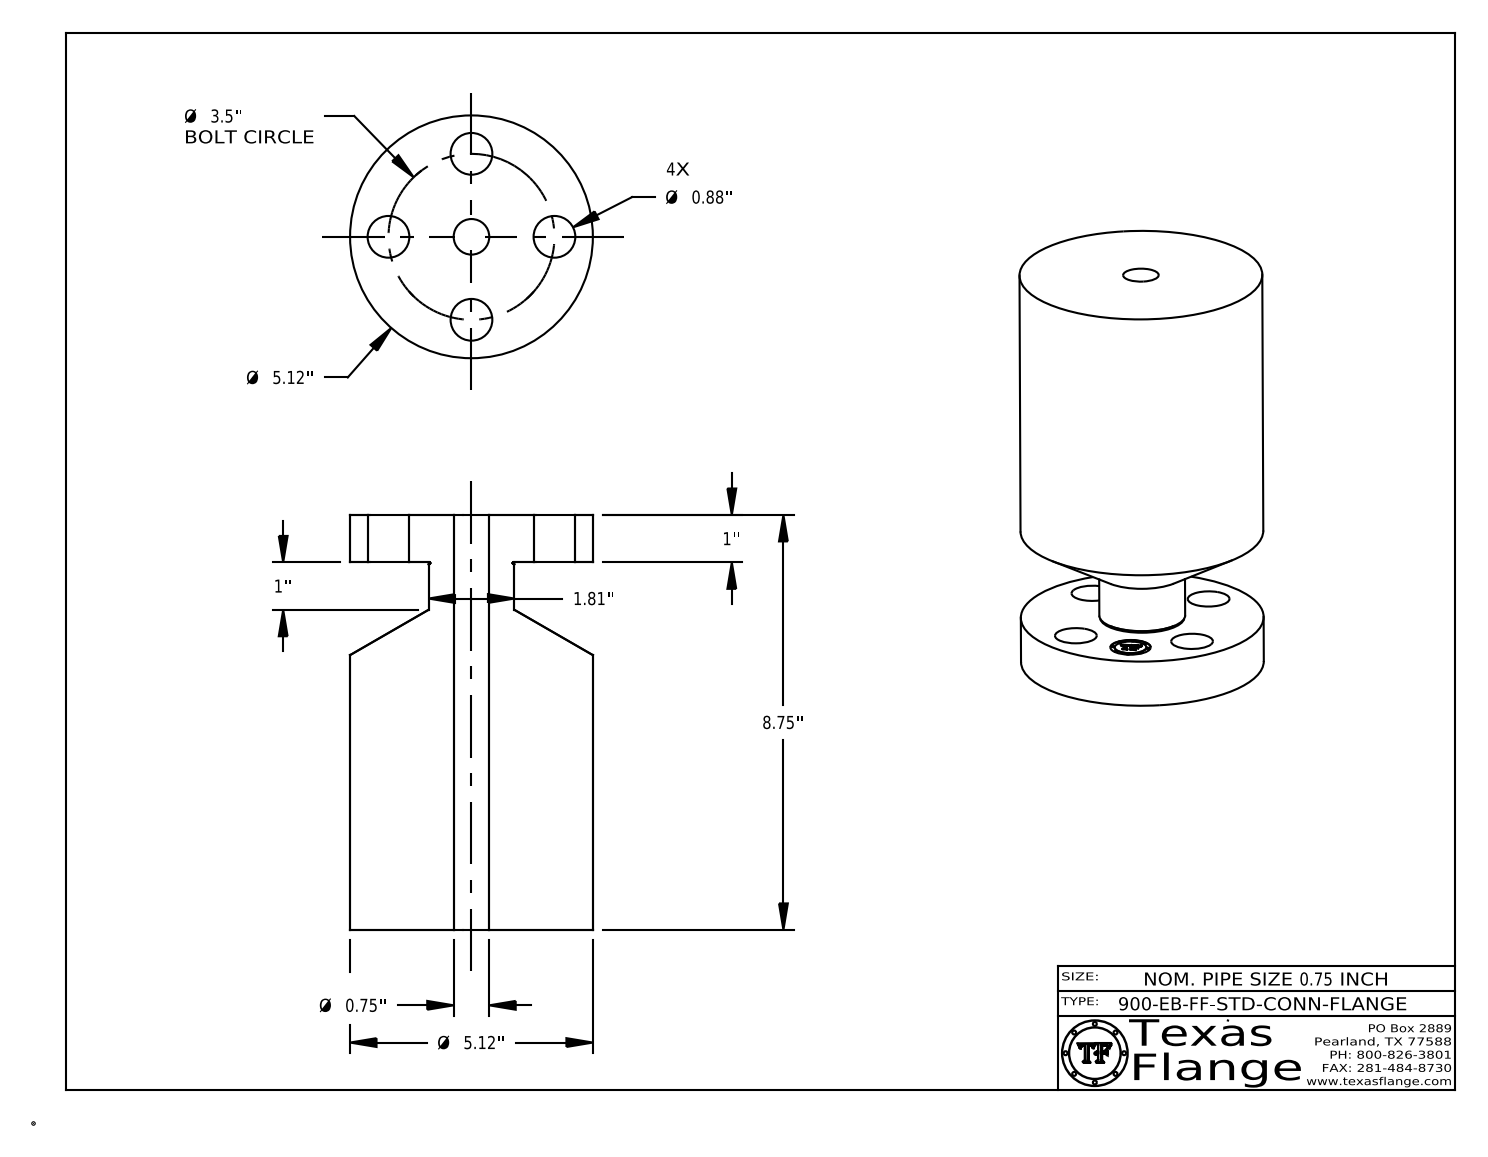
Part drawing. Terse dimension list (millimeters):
name: 0.75-900-EB-FF-STD-CONN-FLANGE
written by: CATIA V5 STEP AP214 (AUTOMOTIVE_DESIGN)
unit: mm
bodies: 1 solid, 410 faces (368 planar, 36 cylindrical, 6 other)
size: 222.3 × 130 × 130
volume: 2 391 000 mm³; area: 142 700 mm²
holes: 4× ⌀22.4, 1× ⌀19.1, 1× ⌀21.6
bosses: 8× ⌀1.3, 1× ⌀130, 1× ⌀46, 1× ⌀17
face distances: 222.3, 25.4, 196.9, 25.3, 197, 0.4, 6.5, 6.3, 1.2, 4.2
hole spacings: 44.5, 62.9, 34, 82.1, 88.9
